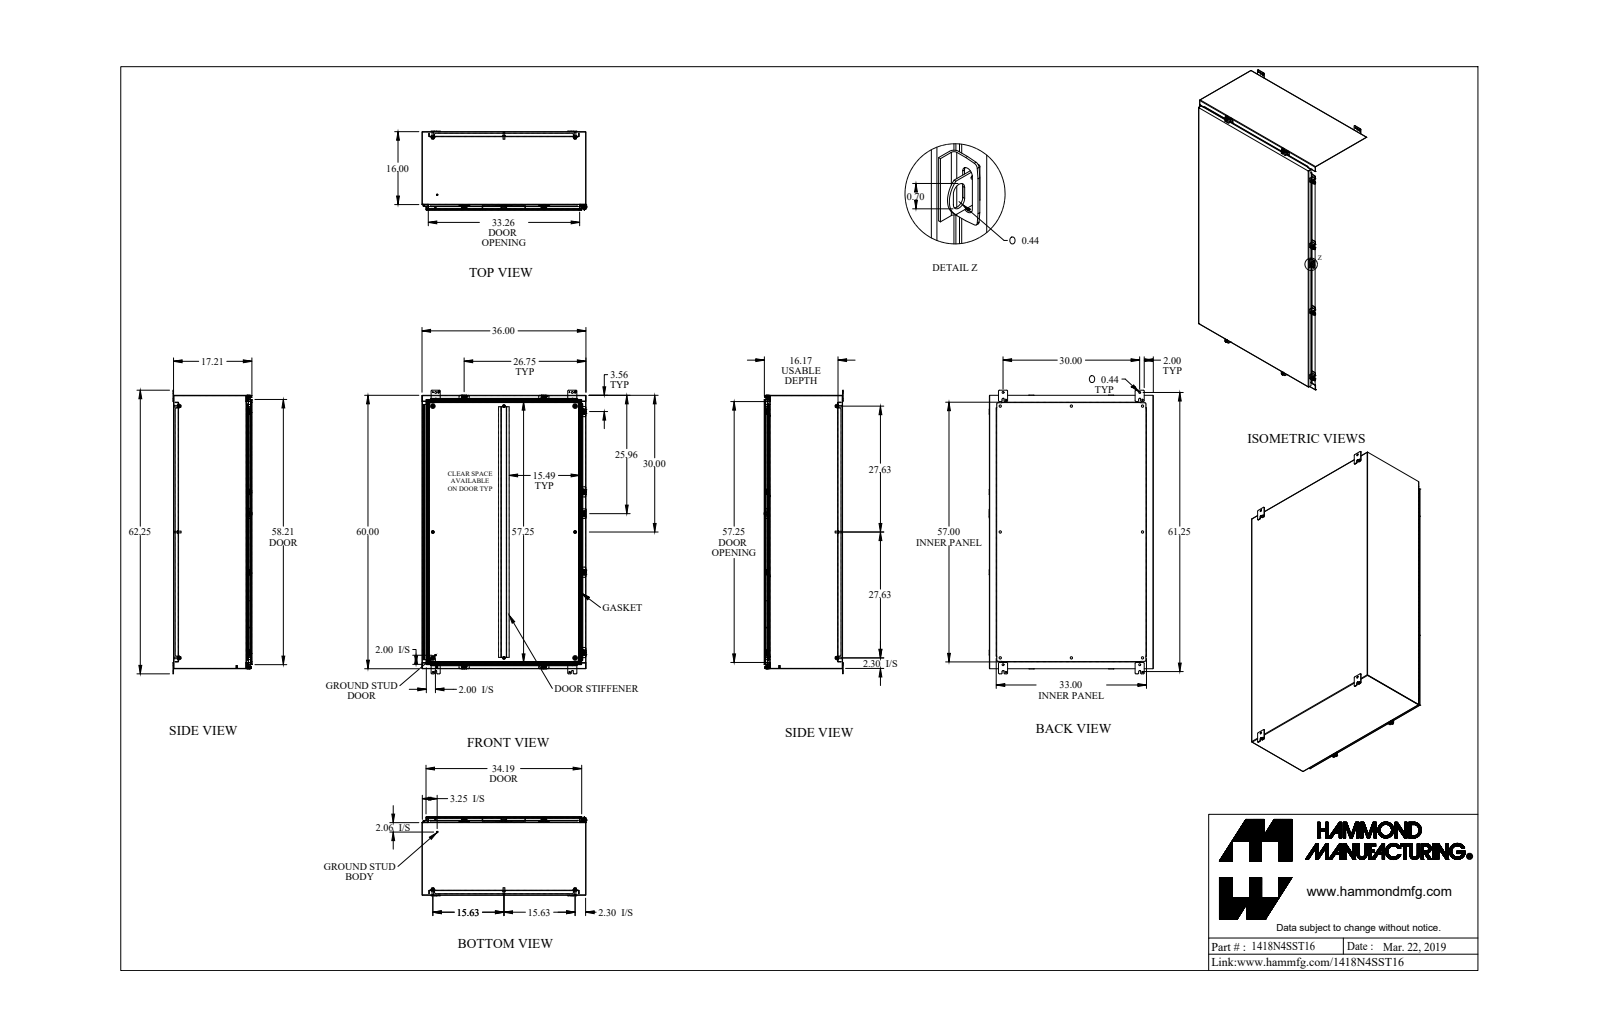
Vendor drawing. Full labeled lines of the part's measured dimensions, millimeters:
Part name (STEP PRODUCT): 1418N4SST16_Default
STEP written by: SolidWorks 2019 (CONFIG_CONTROL_DESIGN)
Units: millimetres
Bodies: 66 solids, 2432 faces (1459 planar, 889 cylindrical, 84 other)
Overall size (bounding box): 1581.2 × 916 × 441.3
Volume: 13 070 000 mm³ · Surface area: 13 490 000 mm²
Round holes (diameter × count): ⌀5.4 ×8, ⌀6.7 ×8, ⌀9.5 ×8, ⌀12.7 ×8, ⌀7.8 ×4, ⌀8 ×4, ⌀11.1 ×4, ⌀11.3 ×4, ⌀3.2 ×1, ⌀4.7 ×1
Round bosses / shafts (diameter × count): ⌀16.5 ×8, ⌀12.7 ×8, ⌀9.9 ×8, ⌀9.5 ×8, ⌀8.4 ×8, ⌀6.2 ×8, ⌀25.4 ×4, ⌀8 ×2
Partial cylindrical surfaces — rounded edges, fillets, slot ends (radius × count): R6.4 ×44, R1.2 ×39, R3.6 ×39, R4.8 ×30, R0.9 ×22, R2.7 ×22, R3.6 ×16, R3.2 ×12
Main face-to-face distances: 1.8, 433.5, 435.3, 1.8, 2.4, 435.3, 437.1, 23.8, 912.6, 25.6
Hole centre spacings: 701.7, 793.8, 1583.4, 1612.3, 182.8, 228.7, 396.9, 621.5
